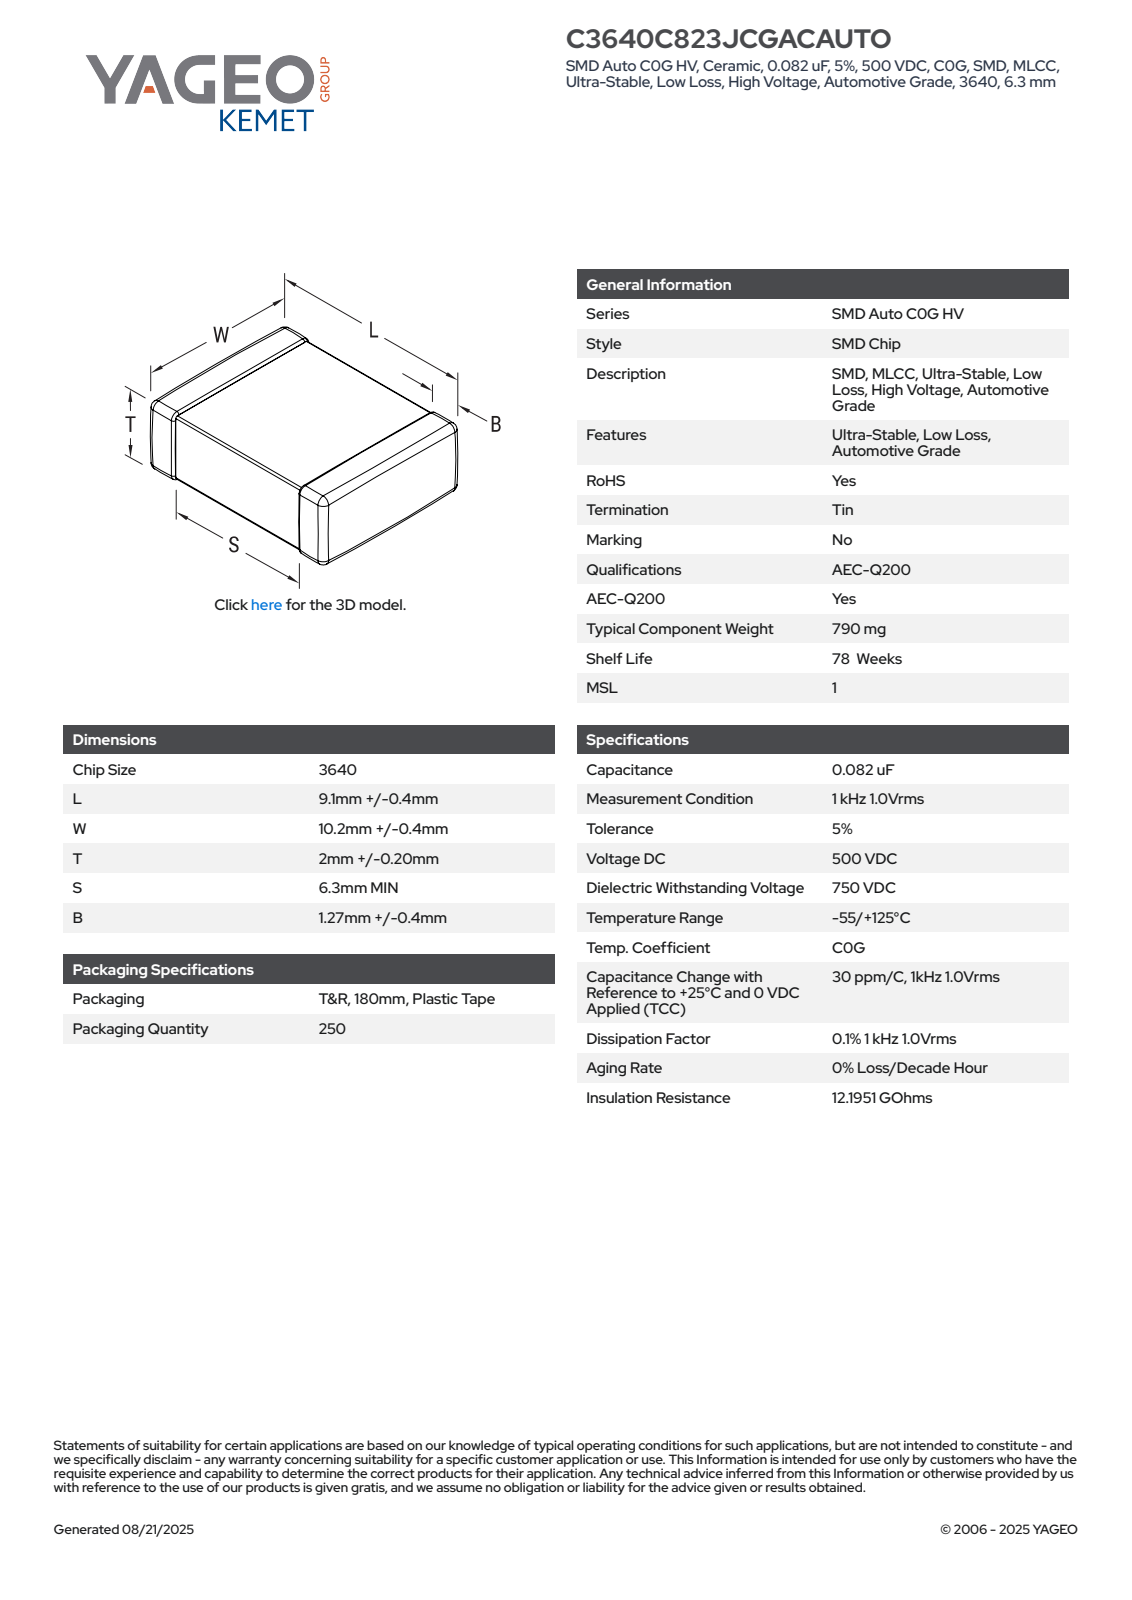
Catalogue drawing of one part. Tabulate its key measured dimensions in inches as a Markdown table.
| quantity | value |
| --- | --- |
| part name | CCS_CCSTD_3640_L9.5W10.6T2.2B1.27 |
| STEP written by | SolidWorks 2021 (AUTOMOTIVE_DESIGN) |
| units | inches |
| bodies | 4 solids, 125 faces (71 planar, 38 cylindrical, 16 other) |
| overall size | 0.417 × 0.374 × 0.087 |
| volume | 0.011 in³ |
| surface area | 0.451 in² |
| partial cylindrical surfaces (radius × count) | 0.009 × 24 |
| main face-to-face distances | 0.069, 0.078, 0.087, 0.374, 0.409, 0.4, 0.417, 0.141, 0.233, 0.202 |
